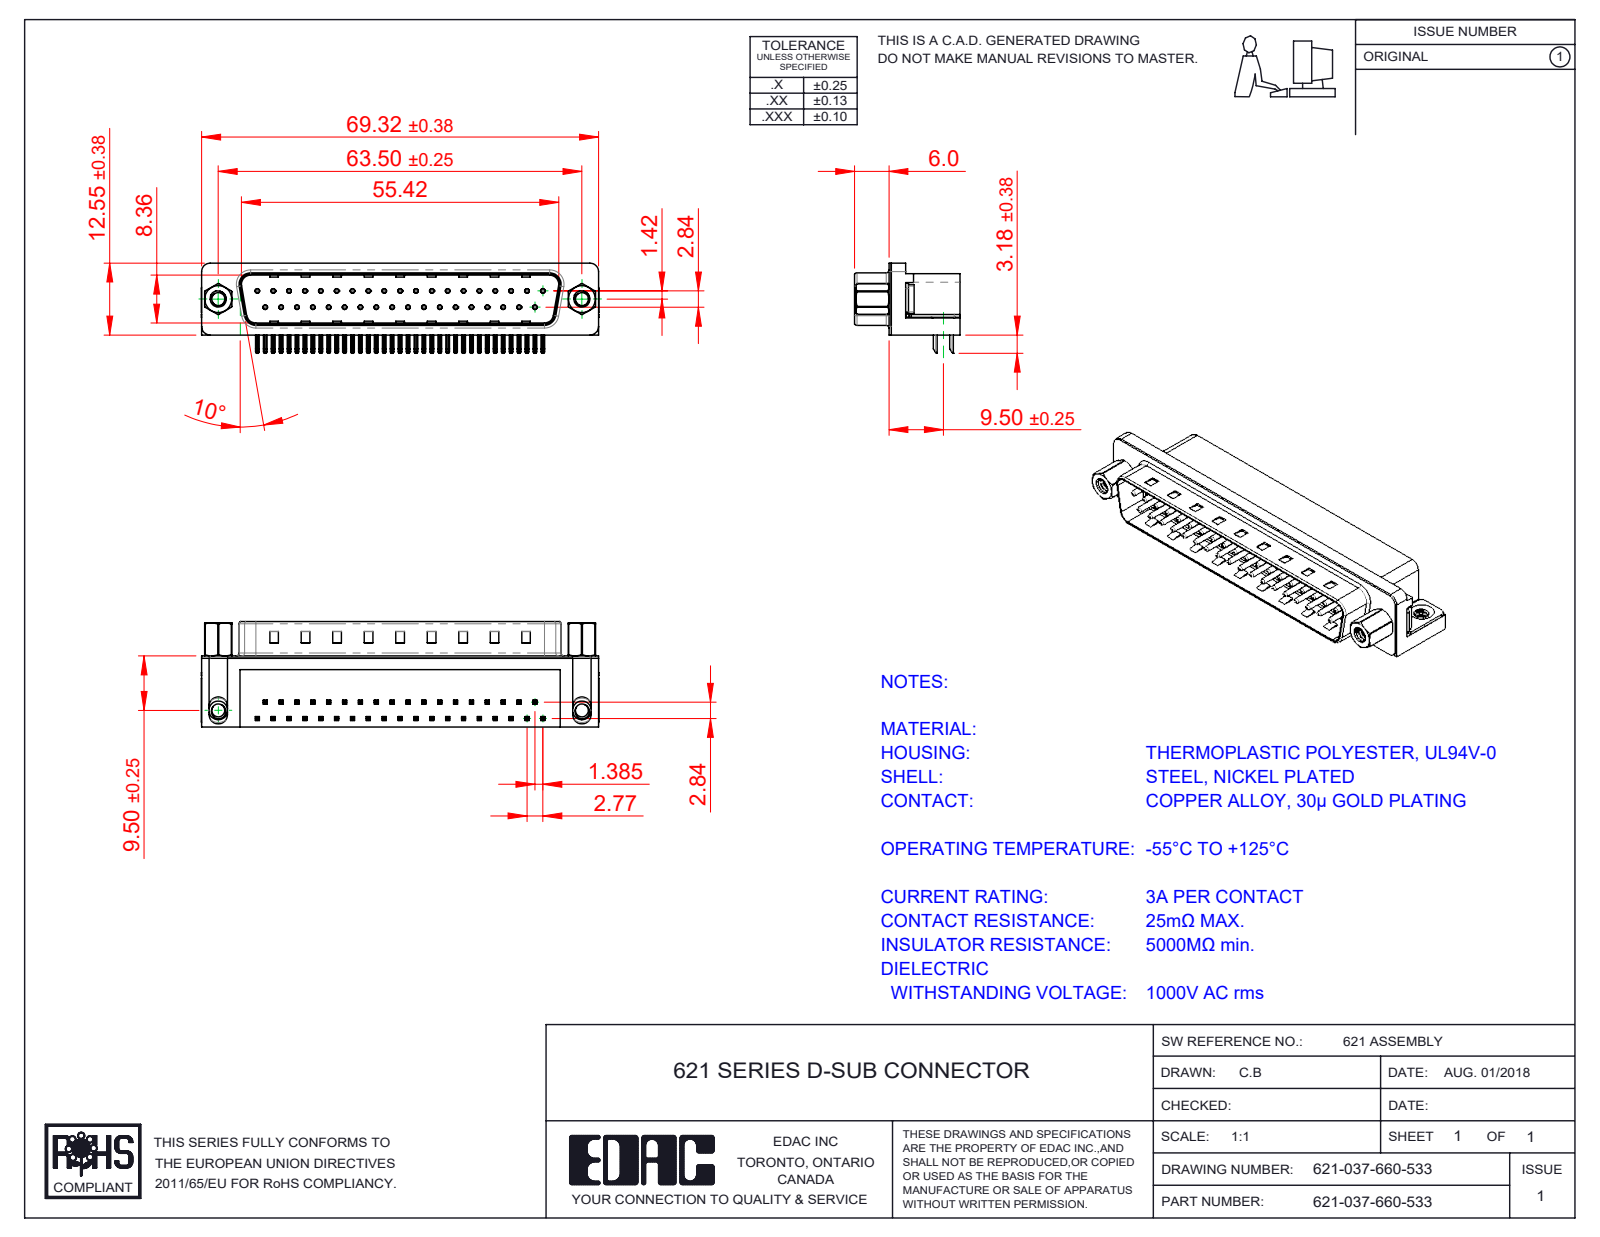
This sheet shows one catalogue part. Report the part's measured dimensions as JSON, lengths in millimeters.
{"part_name": "621 2 Prong Board Lock; 621 4-40 Threaded Rivet; 621-037-660-533; 621 Housing_37 Socket (+4 more)", "step_written_by": "SolidWorks 2016 (CONFIG_CONTROL_DESIGN)", "units": "millimeters", "bodies": {"solids": 45, "faces": 3365, "planar": 2067, "cylindrical": 995, "other": 303}, "overall_size": [69.4, 18.4, 16.25], "volume_mm3": 8834, "surface_area_mm2": 10583, "round_holes": [[0.35, 37], [0.8, 37], [2.26, 2], [2.29, 2], [4, 2], [4.8, 2], [5, 2]], "round_bosses_or_shafts": [[0.75, 37], [4.9, 2], [4.75, 2], [3.9, 2], [2.79, 2]], "partial_cylinders_radius": [[0.25, 156], [0.12, 74], [1, 16], [0.5, 14], [1.6, 8], [1.5, 7], [0.32, 4], [0.9, 4]], "face_to_face_distances": [0.4, 12, 10.35, 8.76, 1.7, 2.1, 10.46, 10.86, 12.4, 9], "hole_center_spacings": [3.16, 2.77, 5.54, 8.31, 11.08, 13.85, 19.39, 22.16]}
